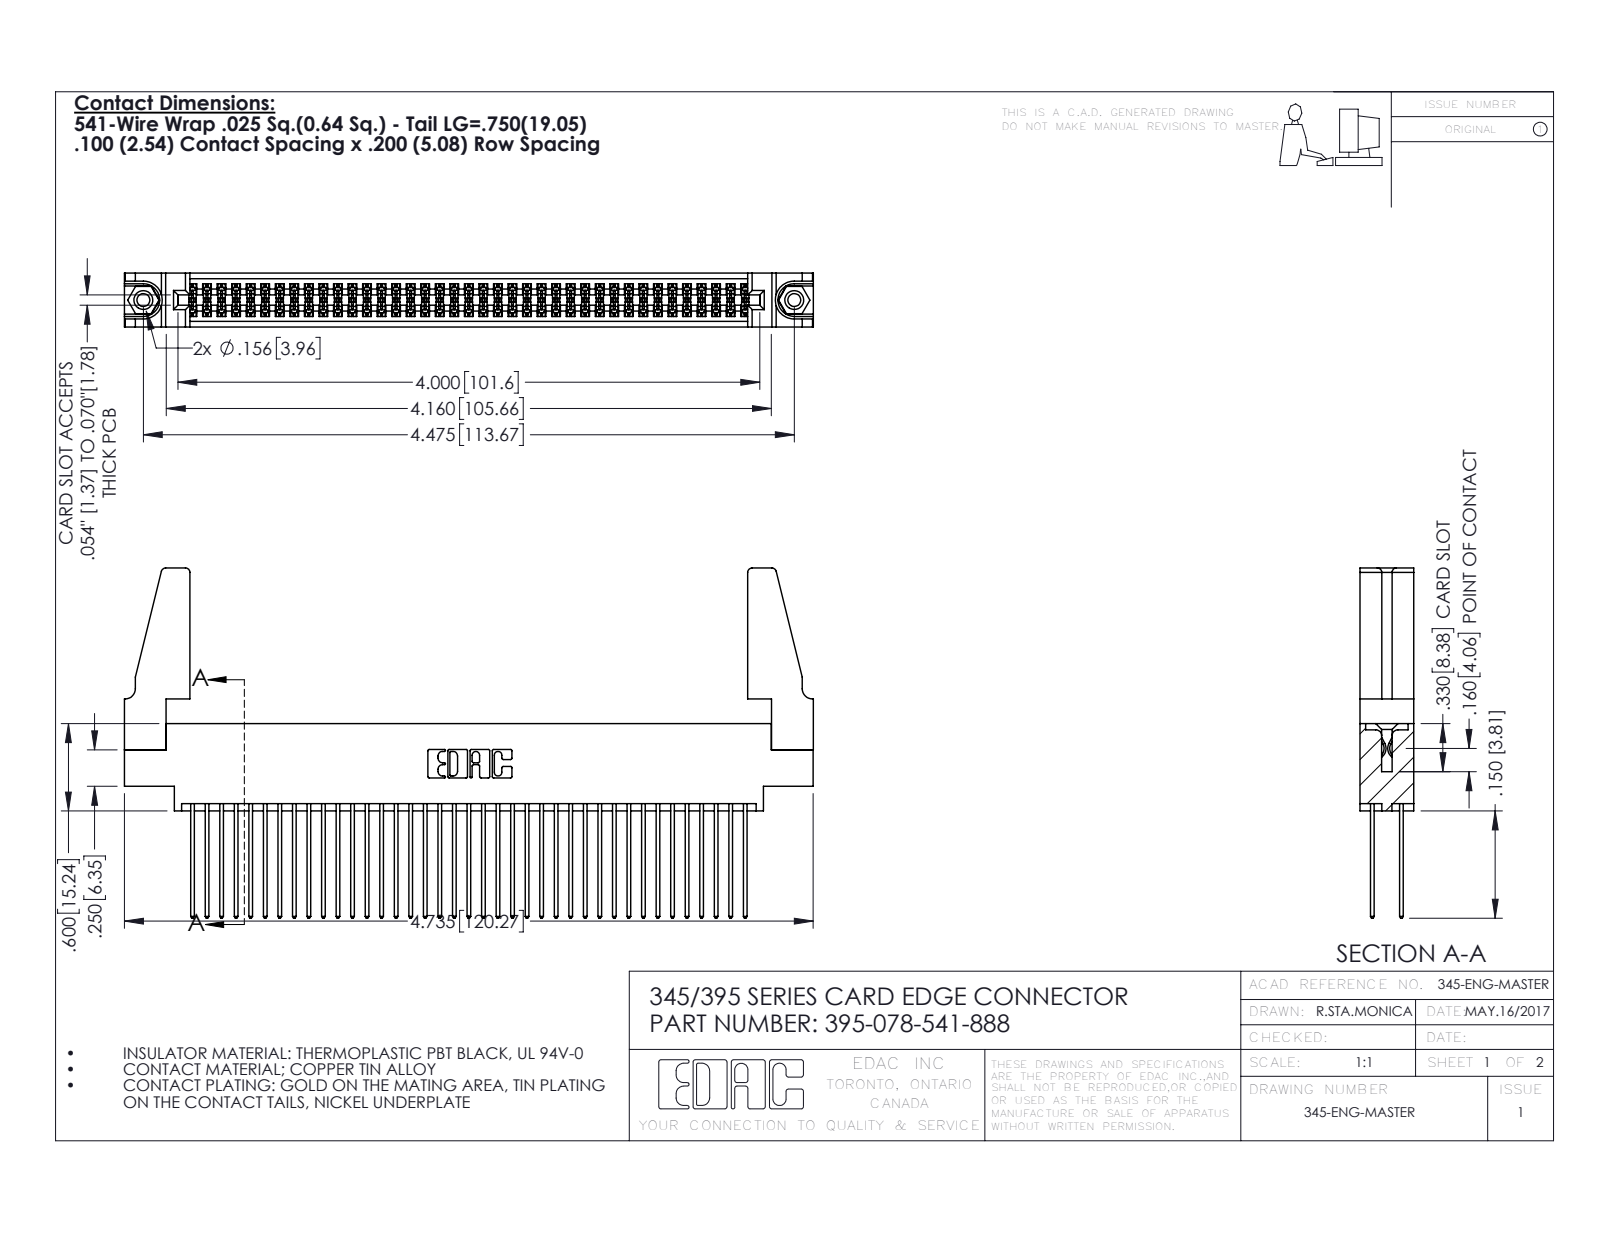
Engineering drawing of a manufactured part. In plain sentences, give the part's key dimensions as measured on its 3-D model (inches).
The part is named "345-250-001_345-250-001-102; 345 Part_0.170 Offset - 0.156 Dia-TH; 395-078-541-888; 345-220-078_345-220-088 (+1 more)". Its 3-D file was written by "SolidWorks 2016 (CONFIG_CONTROL_DESIGN)". It is 83 solids with 4154 faces: 2730 planar, 1408 cylindrical and 16 other. Overall it measures 4.736 by 2.407 by 0.37 inches. Its volume is 0.93 cubic inches and its surface area 35.71 square inches. Round holes: 2 of diameter 0.089, 2 of diameter 0.125, 2 of diameter 0.156, 1 of diameter 0.064. Round bosses or shafts: 2 of diameter 0.155. Partial cylindrical surfaces (rounded edges, fillets, slot ends): 117 of radius 0.006, 78 of radius 0.01, 22 of radius 0.01, 8 of radius 0.03, 6 of radius 0.007, 6 of radius 0.031, 3 of radius 0.026, 2 of radius 0.014. The main face-to-face distances are 0.072, 0.298, 0.2, 0.098, 0.272, 0.025, 0.37, 0.225, 0.175, 0.149. The hole center spacings are 0.27, 4.239, 4.475.
